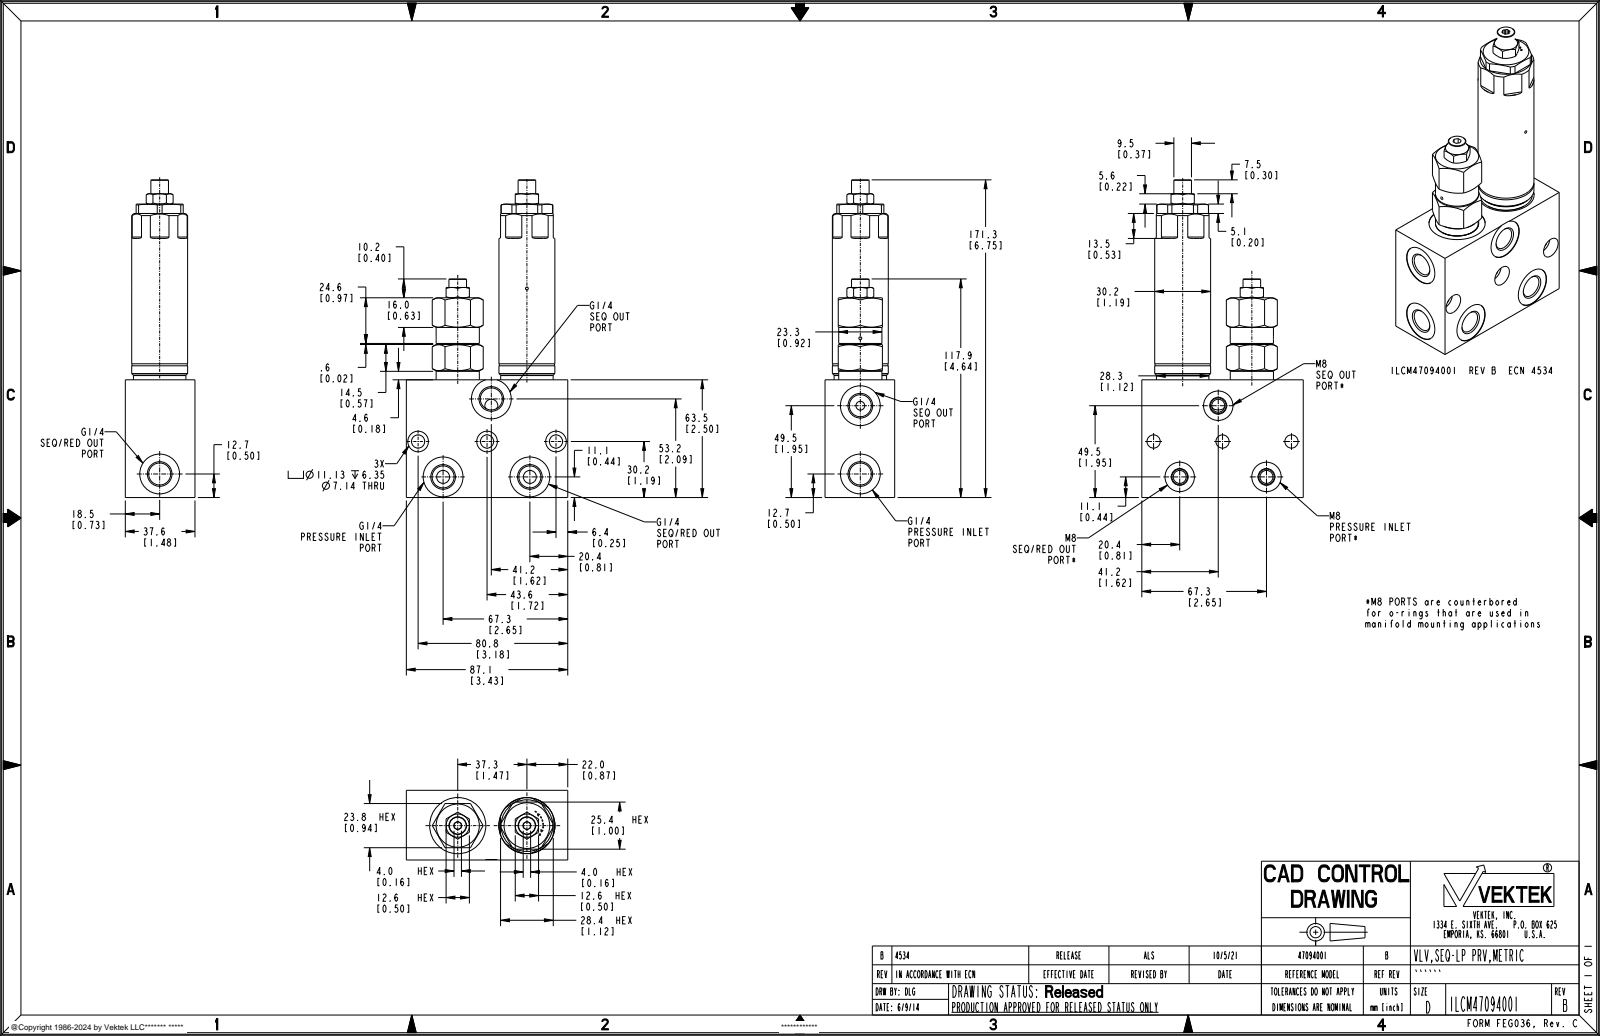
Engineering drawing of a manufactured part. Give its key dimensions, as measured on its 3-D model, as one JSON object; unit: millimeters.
{"part_name": "ILCM47094001", "step_written_by": "PRO/ENGINEER BY PARAMETRIC TECHNOLOGY CORPORATION, 2013320 (CONFIG_CONTROL_DESIGN)", "units": "millimeters", "bodies": {"solids": 2, "faces": 353, "planar": 111, "cylindrical": 135, "other": 107}, "overall_size": [175.67, 87.12, 37.59], "volume_mm3": 272092, "surface_area_mm2": 51785, "round_holes": [[11.89, 5], [21.49, 5], [7.01, 3], [7.14, 3], [11.13, 3], [15.88, 3], [2.41, 2], [9.96, 2], [30.3, 2], [1.57, 1], [2.39, 1], [3.17, 1]], "round_bosses_or_shafts": [[30.18, 1], [28.32, 1], [23.32, 1], [23.3, 1], [20.32, 1], [17.78, 1], [17.4, 1], [15.8, 1]], "partial_cylinders_radius": [[10.87, 1], [14.29, 1]], "face_to_face_distances": [37.59, 63.5, 87.12, 23.82, 37.34, 86.87, 39.65, 23.83, 39.4, 25.4], "hole_center_spacings": [37.21, 1.27, 3.66, 18.17, 18.29, 19.44, 23.08, 23.38]}
